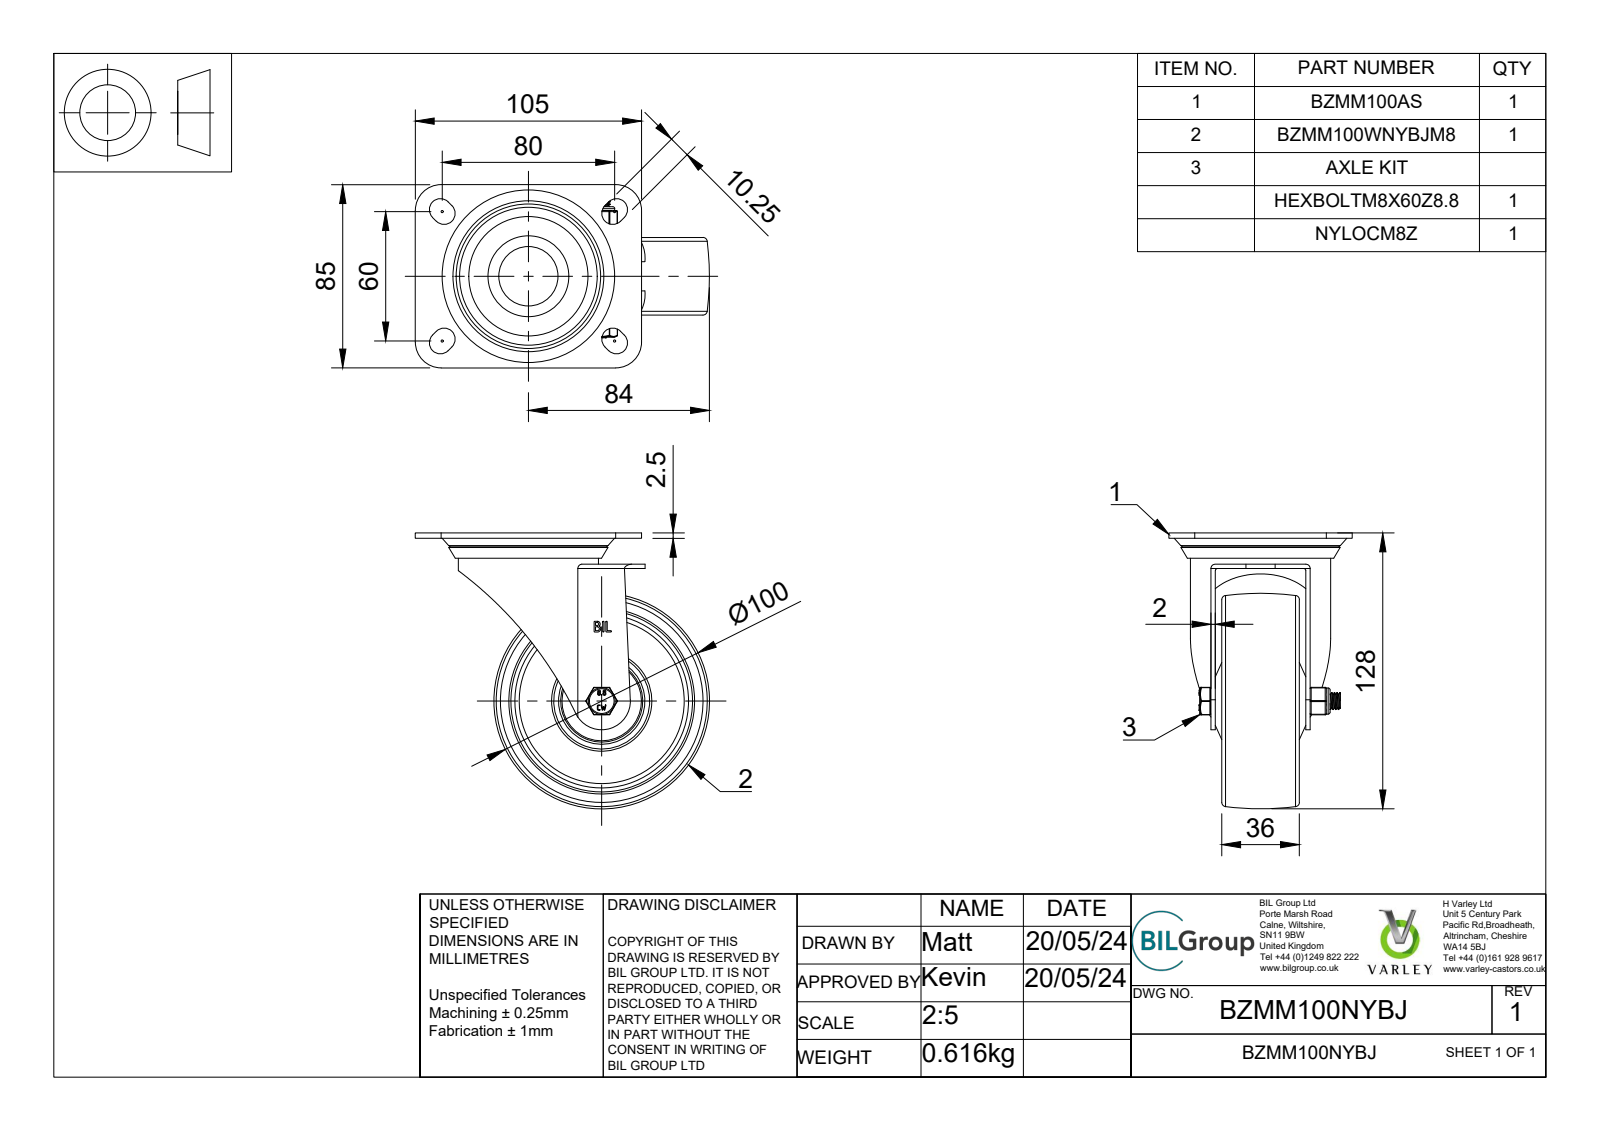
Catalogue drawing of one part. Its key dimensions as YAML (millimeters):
part_name: "BZMM100NYBJ v4; BZMM100AS - 2 - 42 v1; ZINC PLATED, PRESSED STEEL TOP PLATE; ZINC PLATED, PRESSED STEEL TOP PLATE Geometry (+7 more)"
step_written_by: "Autodesk Translation Framework v13.14.0.145 (AUTOMOTIVE_DESIGN)"
units: millimeters
bodies: {solids: 46, faces: 766, planar: 274, cylindrical: 189, other: 303}
overall_size: [136.5, 128, 85]
volume: 209395
surface_area: 113326
round_holes:
  - {diameter: 0.66, count: 2}
  - {diameter: 8, count: 1}
  - {diameter: 8.2, count: 1}
  - {diameter: 8.25, count: 1}
  - {diameter: 8.6, count: 1}
  - {diameter: 15, count: 1}
  - {diameter: 20, count: 1}
  - {diameter: 22.5, count: 1}
  - {diameter: 25, count: 1}
  - {diameter: 27.5, count: 1}
  - {diameter: 30, count: 1}
  - {diameter: 31, count: 1}
round_bosses_or_shafts:
  - {diameter: 65, count: 1}
  - {diameter: 44.5, count: 1}
  - {diameter: 38, count: 1}
  - {diameter: 31.5, count: 1}
  - {diameter: 30.5, count: 1}
  - {diameter: 28, count: 1}
  - {diameter: 23, count: 1}
  - {diameter: 19, count: 1}
partial_cylinders:
  - {radius: 0.5, count: 18}
  - {radius: 0.25, count: 12}
  - {radius: 5.12, count: 8}
  - {radius: 12, count: 5}
  - {radius: 0.33, count: 4}
  - {radius: 0.64, count: 4}
  - {radius: 1, count: 4}
  - {radius: 0.63, count: 2}
face_to_face_distances: [2, 26.75, 17.25, 24.75, 2.5, 7.5, 19.25, 44, 5, 13]
hole_center_spacings: [4.65, 2.49]
